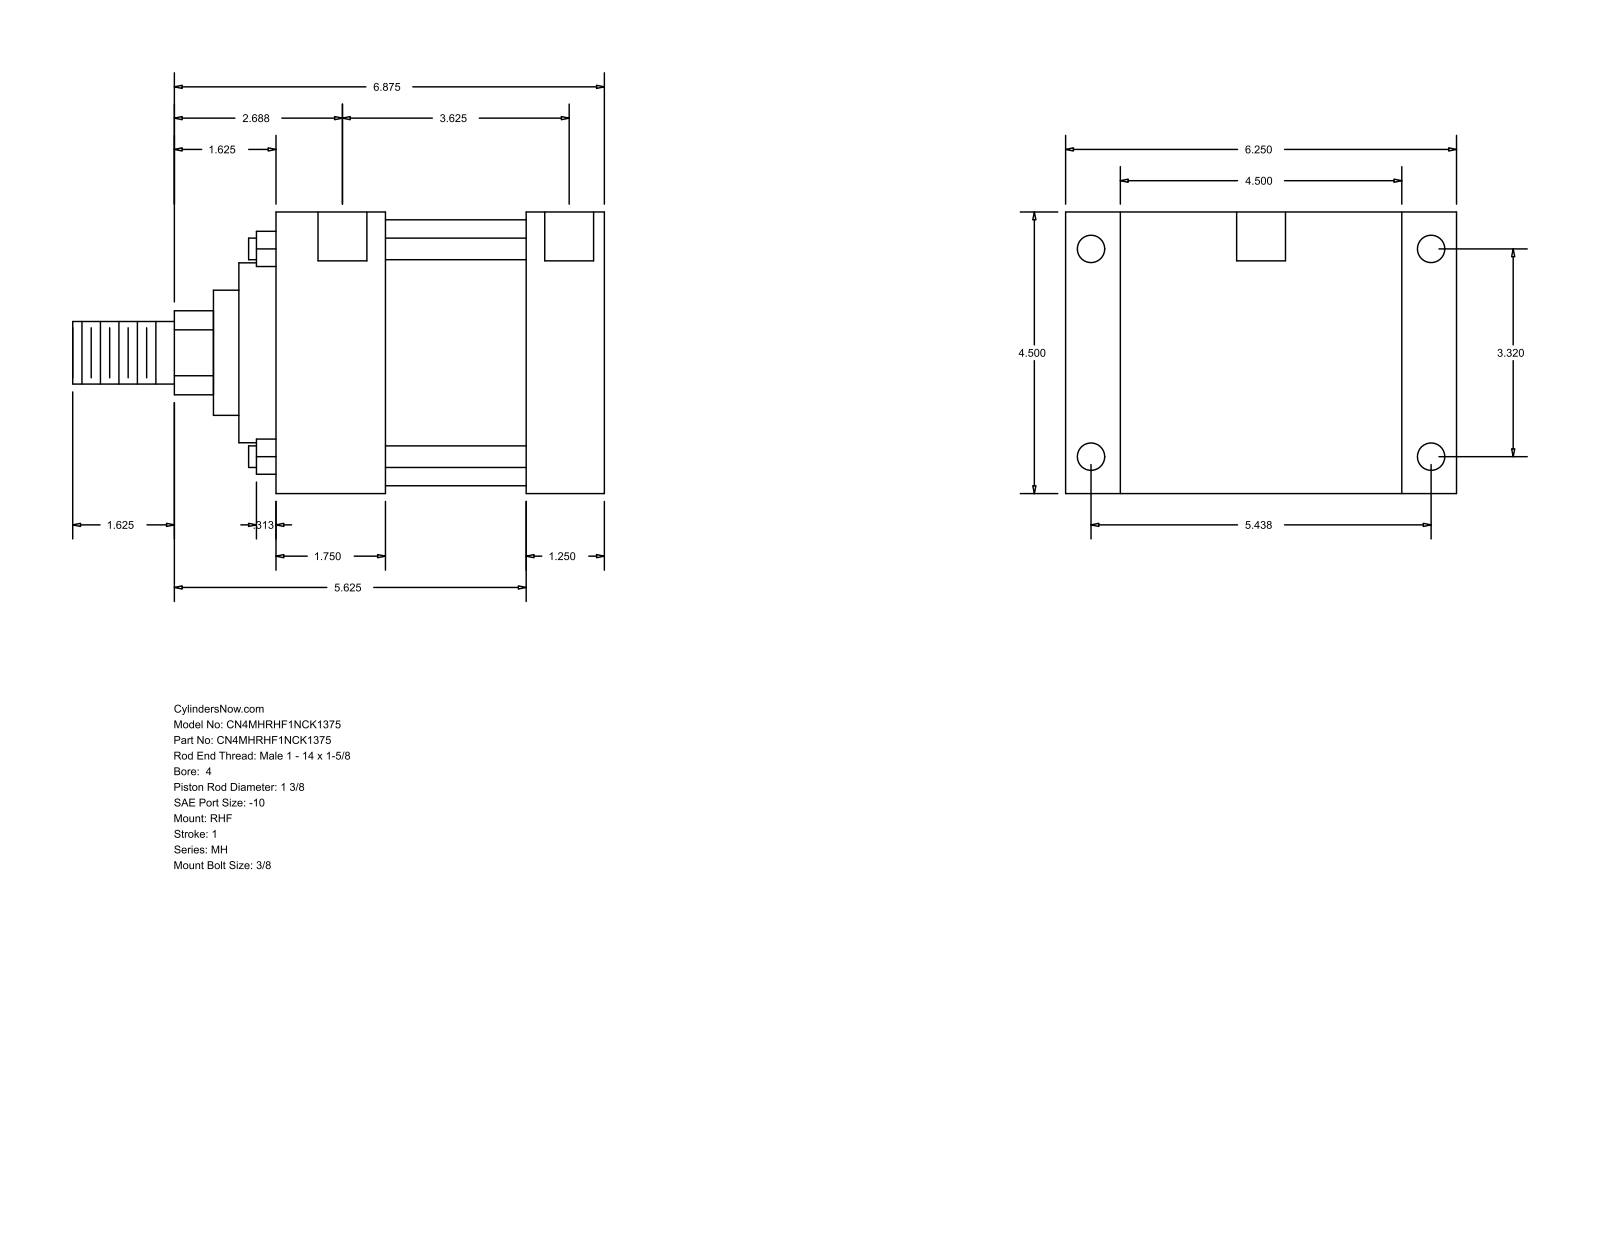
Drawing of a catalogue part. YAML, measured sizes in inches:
part_name: "MH_RHF__0400_1.375"
step_written_by: "GSSL Pune (CONFIG_CONTROL_DESIGN)"
units: inches
bodies: {solids: 0, faces: 90, planar: 61, cylindrical: 29, other: 0}
overall_size: [8.5, 6.25, 4.5]
round_holes:
  - {diameter: 0.344, count: 4}
  - {diameter: 0.438, count: 4}
  - {diameter: 0.781, count: 2}
round_bosses_or_shafts:
  - {diameter: 0.345, count: 4}
  - {diameter: 4.25, count: 1}
  - {diameter: 2.875, count: 1}
  - {diameter: 2, count: 1}
  - {diameter: 1.375, count: 1}
  - {diameter: 1, count: 1}
partial_cylinders:
  - {radius: 0.672, count: 1}
face_to_face_distances: [4.5, 1.25, 4, 5.25, 0.875, 5.375, 1.75, 2.25, 3.5, 6.25]
hole_center_spacings: [0.063, 3.32, 3.688, 3.75, 5.438, 6.371, 3.625]
